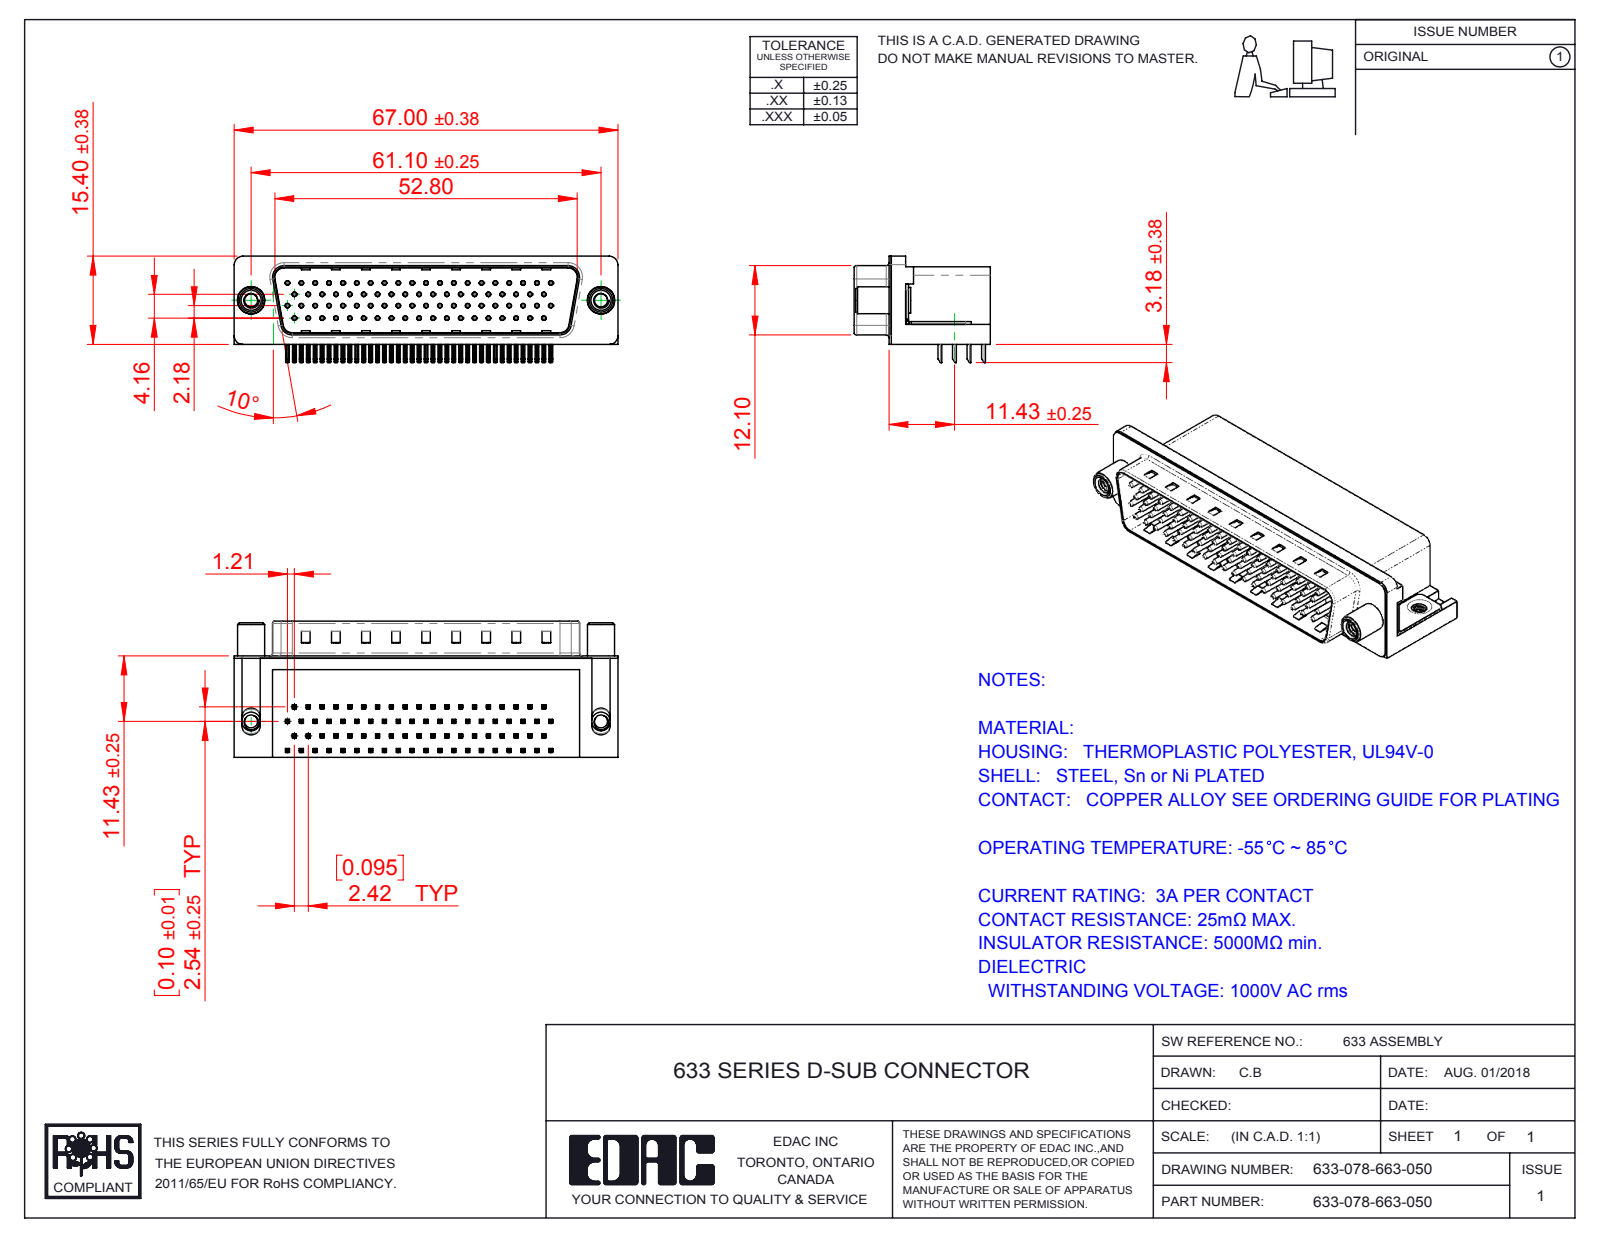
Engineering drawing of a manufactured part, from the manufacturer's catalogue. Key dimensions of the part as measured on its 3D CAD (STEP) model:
Part name (STEP PRODUCT): 633 Housing_78 Contact; 633 4-40 Threaded Board Mount_78 Contact; 633 Shell_78 Contact; 633-078-663-050 (+5 more)
STEP written by: SolidWorks 2016 (CONFIG_CONTROL_DESIGN)
Units: millimetres
Bodies: 84 solids, 6300 faces (3973 planar, 1798 cylindrical, 529 other)
Overall size (bounding box): 67 × 23.8 × 18.58
Volume: 14 715 mm³ · Surface area: 16 627 mm²
Round holes (diameter × count): ⌀0.35 ×78, ⌀0.8 ×78, ⌀2.26 ×2, ⌀2.3 ×2, ⌀3.1 ×2, ⌀4 ×2, ⌀4.8 ×2, ⌀5 ×2
Round bosses / shafts (diameter × count): ⌀0.75 ×78, ⌀4.9 ×2, ⌀4.7 ×2, ⌀4.5 ×2, ⌀3.85 ×2, ⌀3.26 ×2
Partial cylindrical surfaces — rounded edges, fillets, slot ends (radius × count): R0.25 ×312, R0.12 ×156, R1 ×16, R0.5 ×9, R1.6 ×8, R1.5 ×6, R0.45 ×4, R0.9 ×4
Main face-to-face distances: 0.4, 13.2, 17.3, 11.7, 13.35, 2.05, 13.75, 1.65, 1.85, 11.9
Hole centre spacings: 2.42, 4.84, 7.26, 9.68, 6.26, 7.13, 12.1, 8.62
